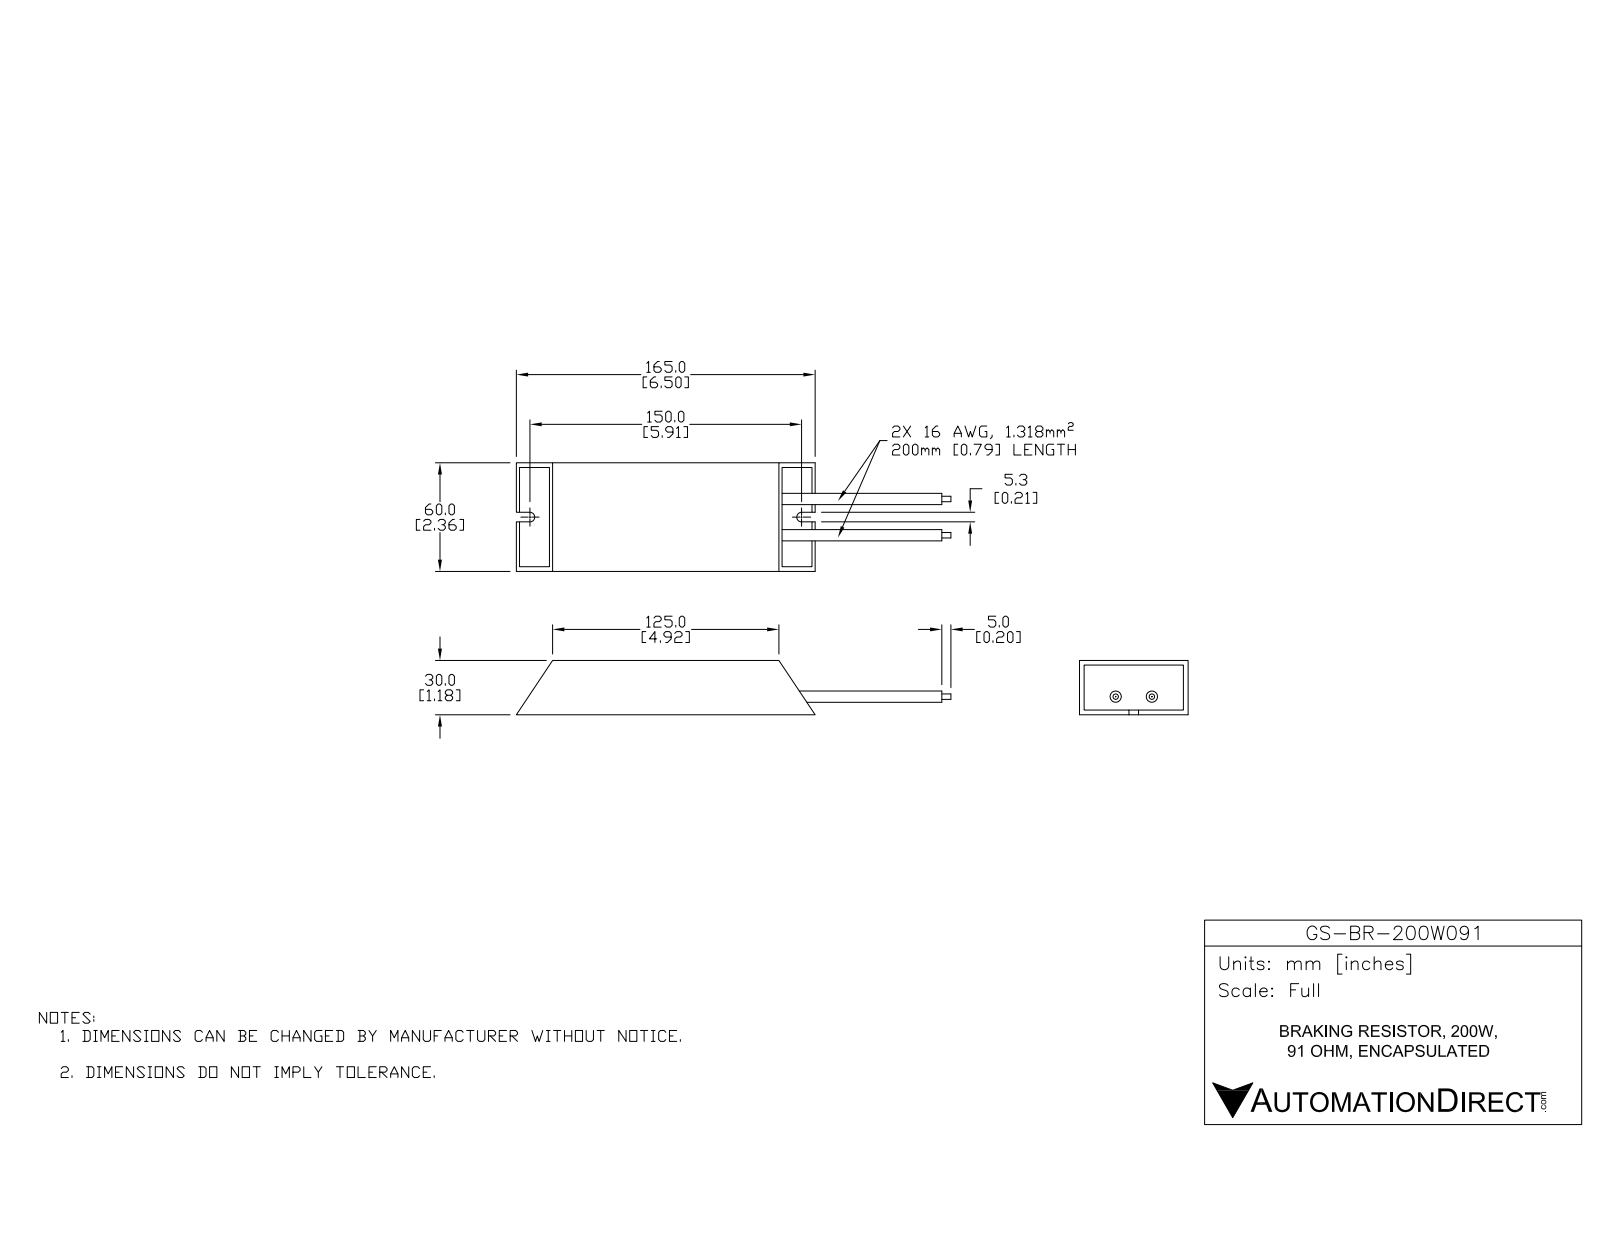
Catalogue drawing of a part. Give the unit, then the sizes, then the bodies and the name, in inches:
Units: inches
Overall size (bounding box): 9.449 × 2.362 × 1.181
Round bosses / shafts (diameter × count): ⌀0.244 ×2, ⌀0.118 ×2
Partial cylindrical surfaces — rounded edges, fillets, slot ends (radius × count): R0.104 ×2
Main face-to-face distances: 1.181, 2.362, 0.102, 1.079, 4.921, 2.26, 2.157, 0.976, 1.077, 1.285
Volume: 14.59 in³ · Surface area: 56.66 in²
Bodies: 1 solid, 34 faces (24 planar, 10 cylindrical, 0 other)
Part name (STEP PRODUCT): GS-BR-200W091
STEP written by: SolidWorks 2015 (AUTOMOTIVE_DESIGN)
